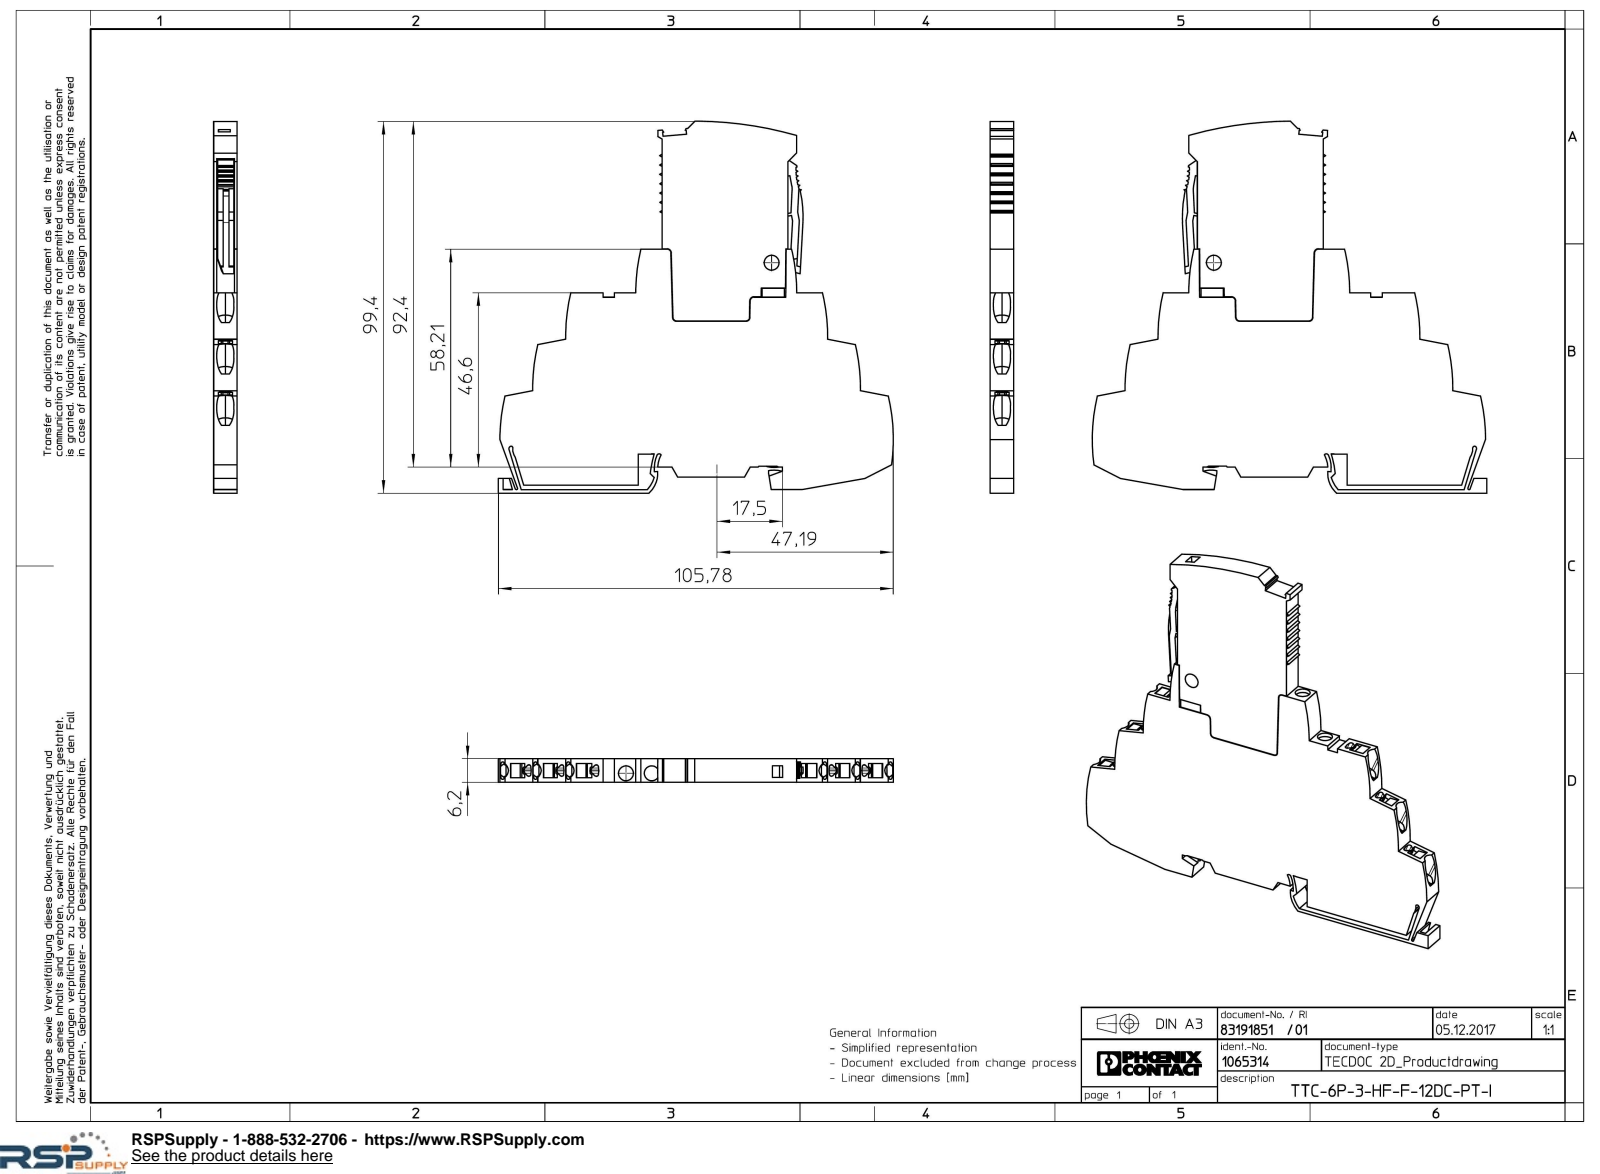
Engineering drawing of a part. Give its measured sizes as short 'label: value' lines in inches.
name: TTC_6P...PT-I-select
written by: Creo Elements/Direct Modeling 20.1A 29-Sep-2018 (C) Parametric Technology GmbH (AUTOMOTIVE_DESIGN)
unit: in
bodies: 1 solid, 485 faces (340 planar, 129 cylindrical, 16 other)
size: 4.165 × 3.913 × 0.248
volume: 2.3 in³; area: 26.96 in²
holes: 1× ⌀0.157
rounds: 24× R0.094, 19× R0.02, 16× R0.039, 12× R0.031, 8× R1.969, 6× R0.07, 6× R0.216, 2× R0.035
face distances: 0.248, 0.035, 0.085, 0.05, 0.134, 0.084, 0.169, 0.033, 0.039, 0.183
